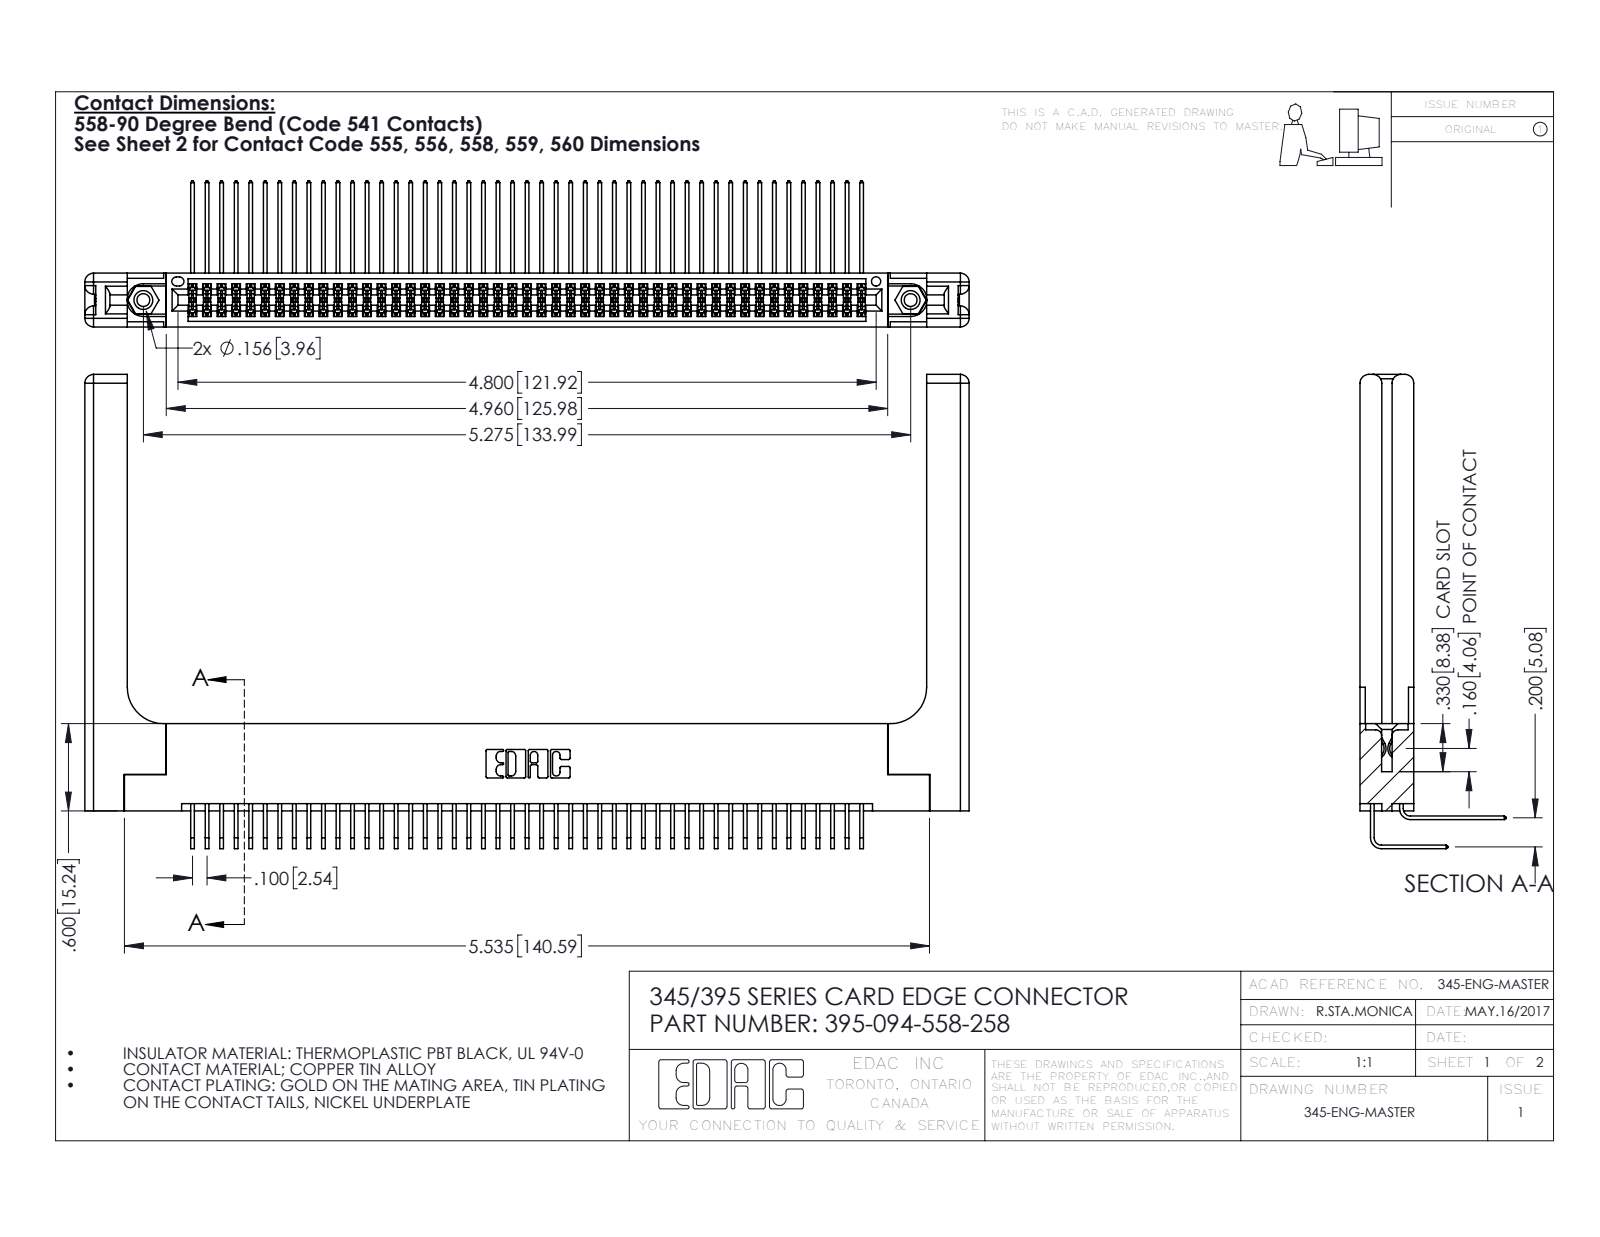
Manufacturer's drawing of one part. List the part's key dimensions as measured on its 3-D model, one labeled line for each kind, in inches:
Part name (STEP PRODUCT): 345-292-001_558 559 Tail - 1; 345-292-001_558 Tail - 2; 345-220-058_345-220-058; 395-094-558-258 (+2 more)
STEP written by: SolidWorks 2016 (CONFIG_CONTROL_DESIGN)
Units: inches
Bodies: 99 solids, 5270 faces (3518 planar, 1692 cylindrical, 60 other)
Overall size (bounding box): 6.079 × 3.259 × 1.005
Volume: 1.468 in³ · Surface area: 47.66 in²
Round holes (diameter × count): ⌀0.089 ×2, ⌀0.125 ×2, ⌀0.156 ×2, ⌀0.064 ×1
Round bosses / shafts (diameter × count): ⌀0.155 ×2
Partial cylindrical surfaces — rounded edges, fillets, slot ends (radius × count): R0.006 ×142, R0.01 ×22, R0.06 ×16, R0.007 ×6, R0.031 ×6, R0.026 ×3, R0.014 ×2, R0.019 ×2
Main face-to-face distances: 0.072, 0.298, 0.37, 0.2, 0.098, 0.272, 0.025, 0.225, 0.148, 0.15
Hole centre spacings: 0.27, 5.039, 5.275
